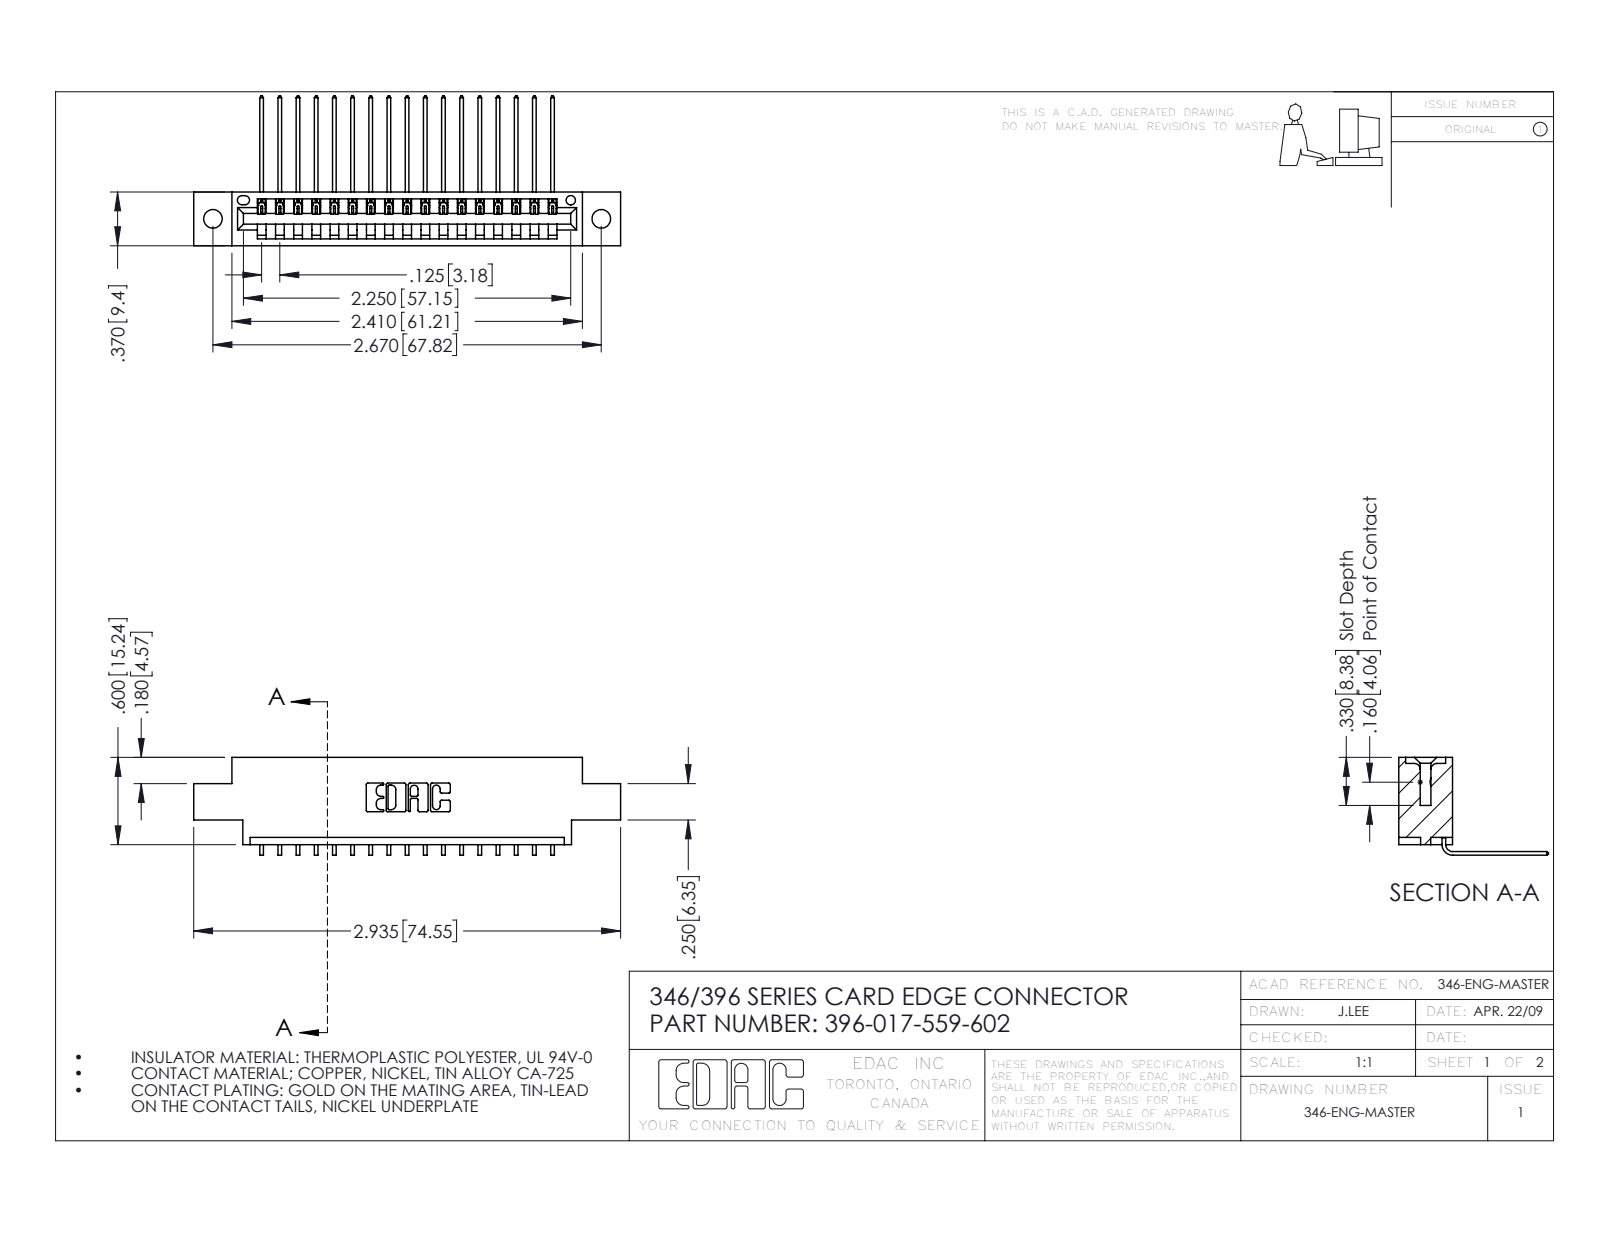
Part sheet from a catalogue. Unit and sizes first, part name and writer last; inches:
Units: inches
Overall size (bounding box): 2.935 × 1.03 × 0.673
Round holes (diameter × count): ⌀0.128 ×2, ⌀0.064 ×1
Partial cylindrical surfaces — rounded edges, fillets, slot ends (radius × count): R0.006 ×34, R0.01 ×22, R0.007 ×6, R0.031 ×6, R0.026 ×3, R0.031 ×2, R0.04 ×2, R0.014 ×1
Main face-to-face distances: 0.048, 0.37, 0.322, 0.25, 0.025, 0.072, 0.148, 0.222, 0.1, 0.174
Hole centre spacings: 0.246, 2.463, 2.67
Volume: 0.417 in³ · Surface area: 13.16 in²
Bodies: 18 solids, 1146 faces (794 planar, 352 cylindrical, 0 other)
Part name (STEP PRODUCT): 346 Part_0.170 Offset - 0.128 Dia; 345-292-001_558 559 Tail - 1; 396-017-559-602
STEP written by: SolidWorks 2016 (CONFIG_CONTROL_DESIGN)
